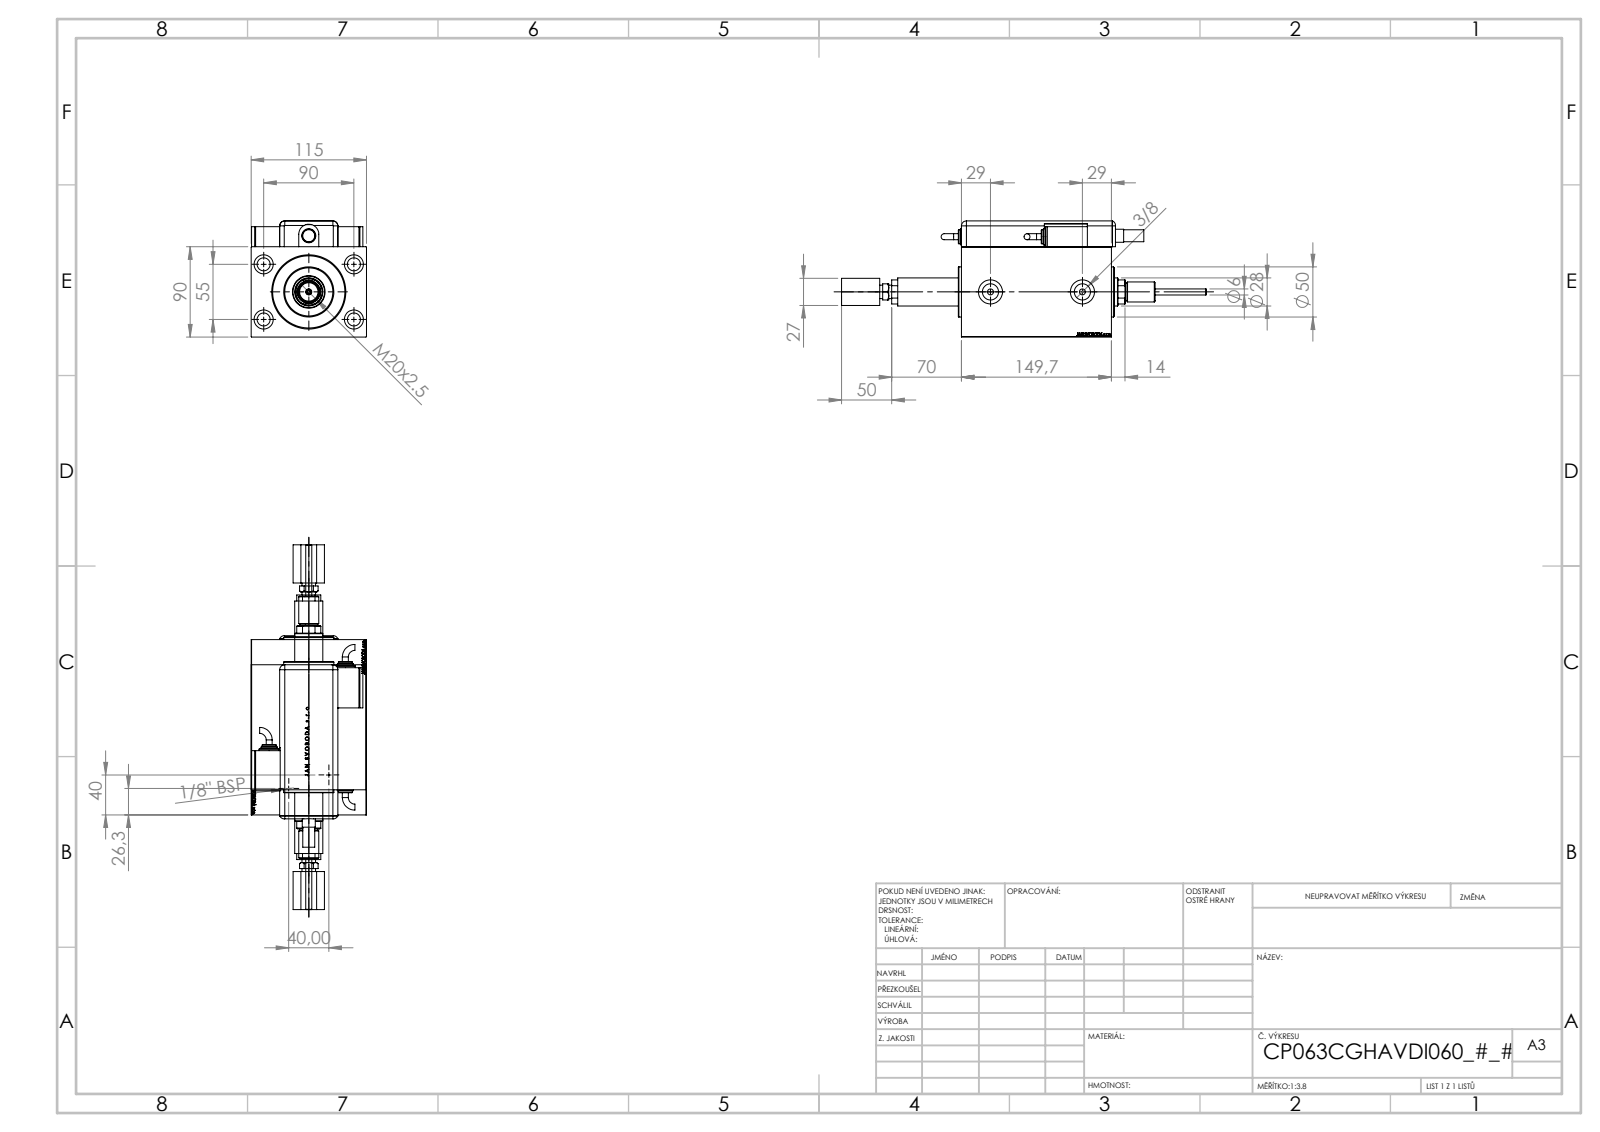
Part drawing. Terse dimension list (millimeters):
name: SWITCH Q; TYC; V450CP_MALE_METRIC; V450DCP_VC_B (+6 more)
written by: SolidWorks 2019 (CONFIG_CONTROL_DESIGN)
unit: mm
bodies: 11 solids, 1306 faces (626 planar, 149 cylindrical, 531 other)
size: 363.7 × 115.8 × 115
volume: 1 531 000 mm³; area: 265 342 mm²
holes: 4× ⌀4, 4× ⌀13, 4× ⌀19, 3× ⌀6, 2× ⌀8, 2× ⌀9.73, 2× ⌀15, 2× ⌀16.17, 2× ⌀24, 1× ⌀3, 1× ⌀14, 1× ⌀18.5
bosses: 3× ⌀20, 2× ⌀16, 2× ⌀14, 2× ⌀6, 1× ⌀50, 1× ⌀18, 1× ⌀13.47, 1× ⌀13
rounds: 9× R5, 1× R10, 1× R13.5
face distances: 90, 3, 115, 149.7, 1, 25.8, 115.8, 17.5, 132.2, 112.8
hole spacings: 52.74, 53.27, 55, 90, 94.85, 105.48, 20, 22.18
